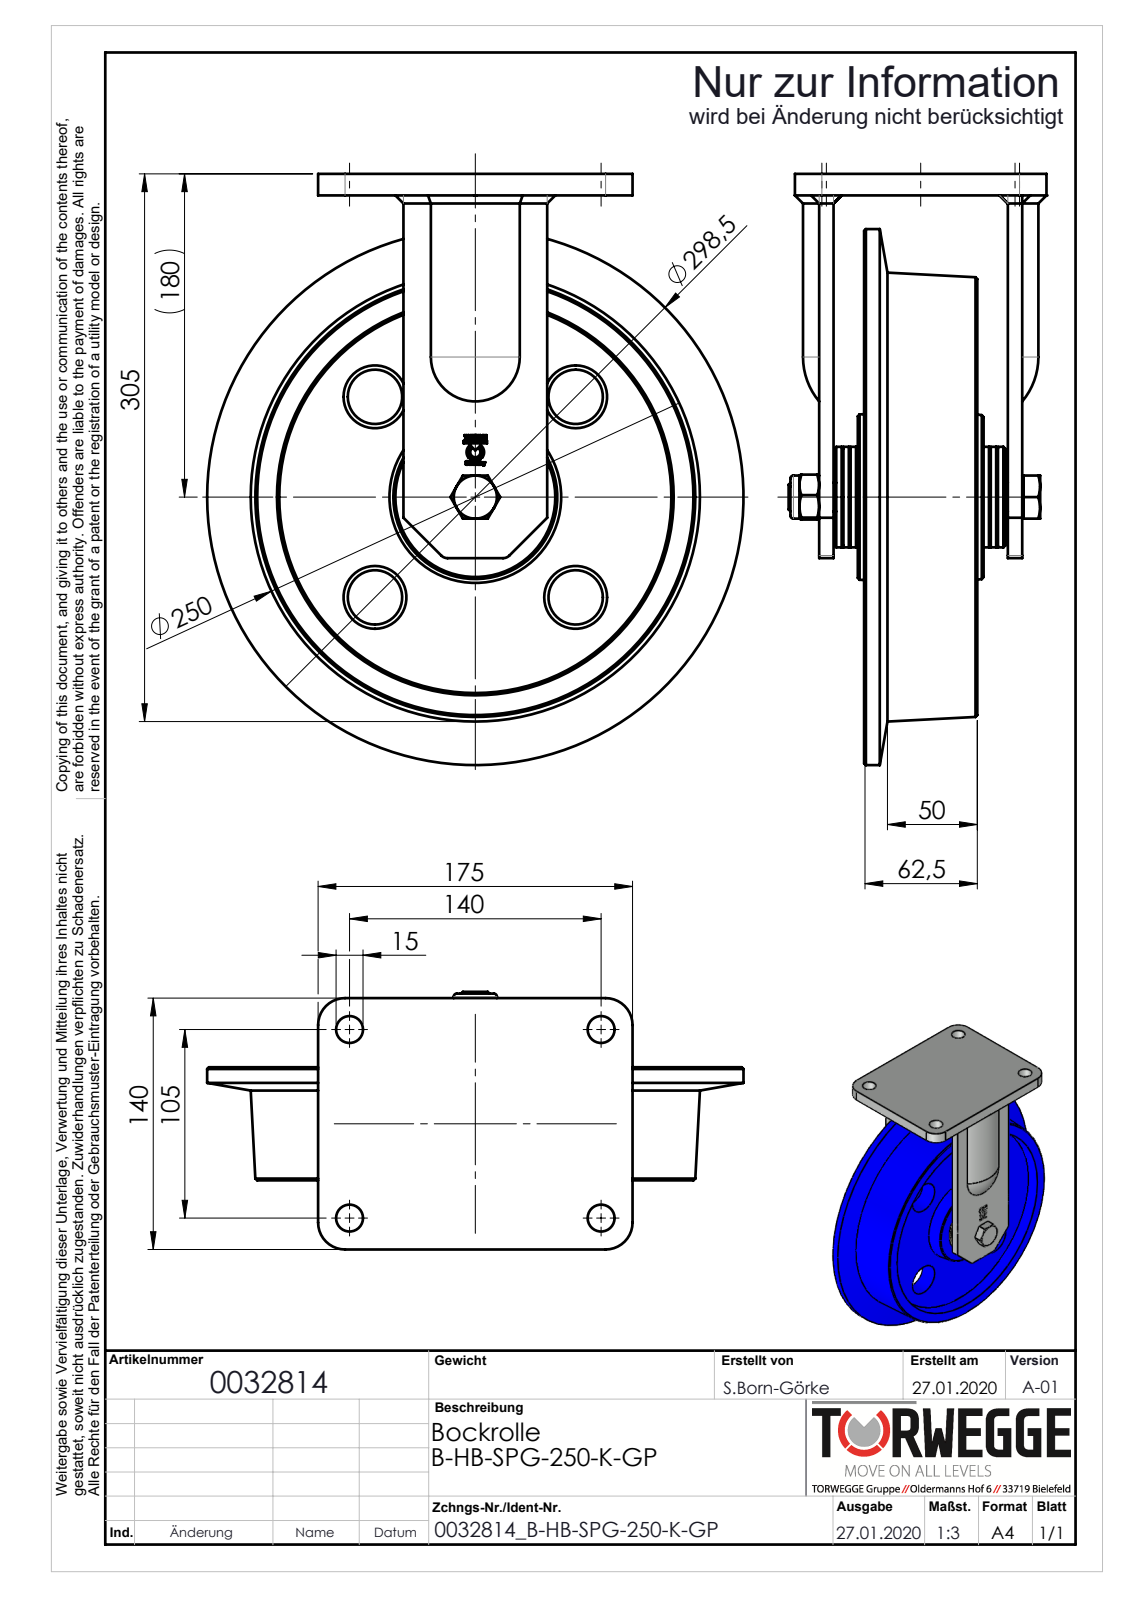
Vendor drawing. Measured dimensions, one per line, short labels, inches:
name: 0032814_B-HB-SPG-250-K-GP_(A-01)
written by: SolidWorks 2018 (AUTOMOTIVE_DESIGN)
unit: in
bodies: 24 solids, 885 faces (379 planar, 162 cylindrical, 344 other)
size: 12.963 × 11.752 × 5.65
volume: 146 in³; area: 750 in²
holes: 4× ⌀0.591, 2× ⌀0.224, 1× ⌀0.551, 1× ⌀0.63, 1× ⌀0.65, 1× ⌀0.72, 1× ⌀0.984, 1× ⌀1.181, 1× ⌀1.22, 1× ⌀1.969, 1× ⌀2.03, 1× ⌀2.107
bosses: 1× ⌀11.752, 1× ⌀2.205, 1× ⌀1.592, 1× ⌀1.515, 1× ⌀0.945
rounds: 4× R0.591, 4× R0.787, 2× R0.197, 2× R1.201, 2× R1.516, 1× R0.154, 1× R0.193
face distances: 0.315, 1.318, 0.472, 1.979, 0.661, 0.531, 4.134, 3.15, 3.602, 0.984
hole spacings: 4.134, 5.512, 6.89, 0.984
